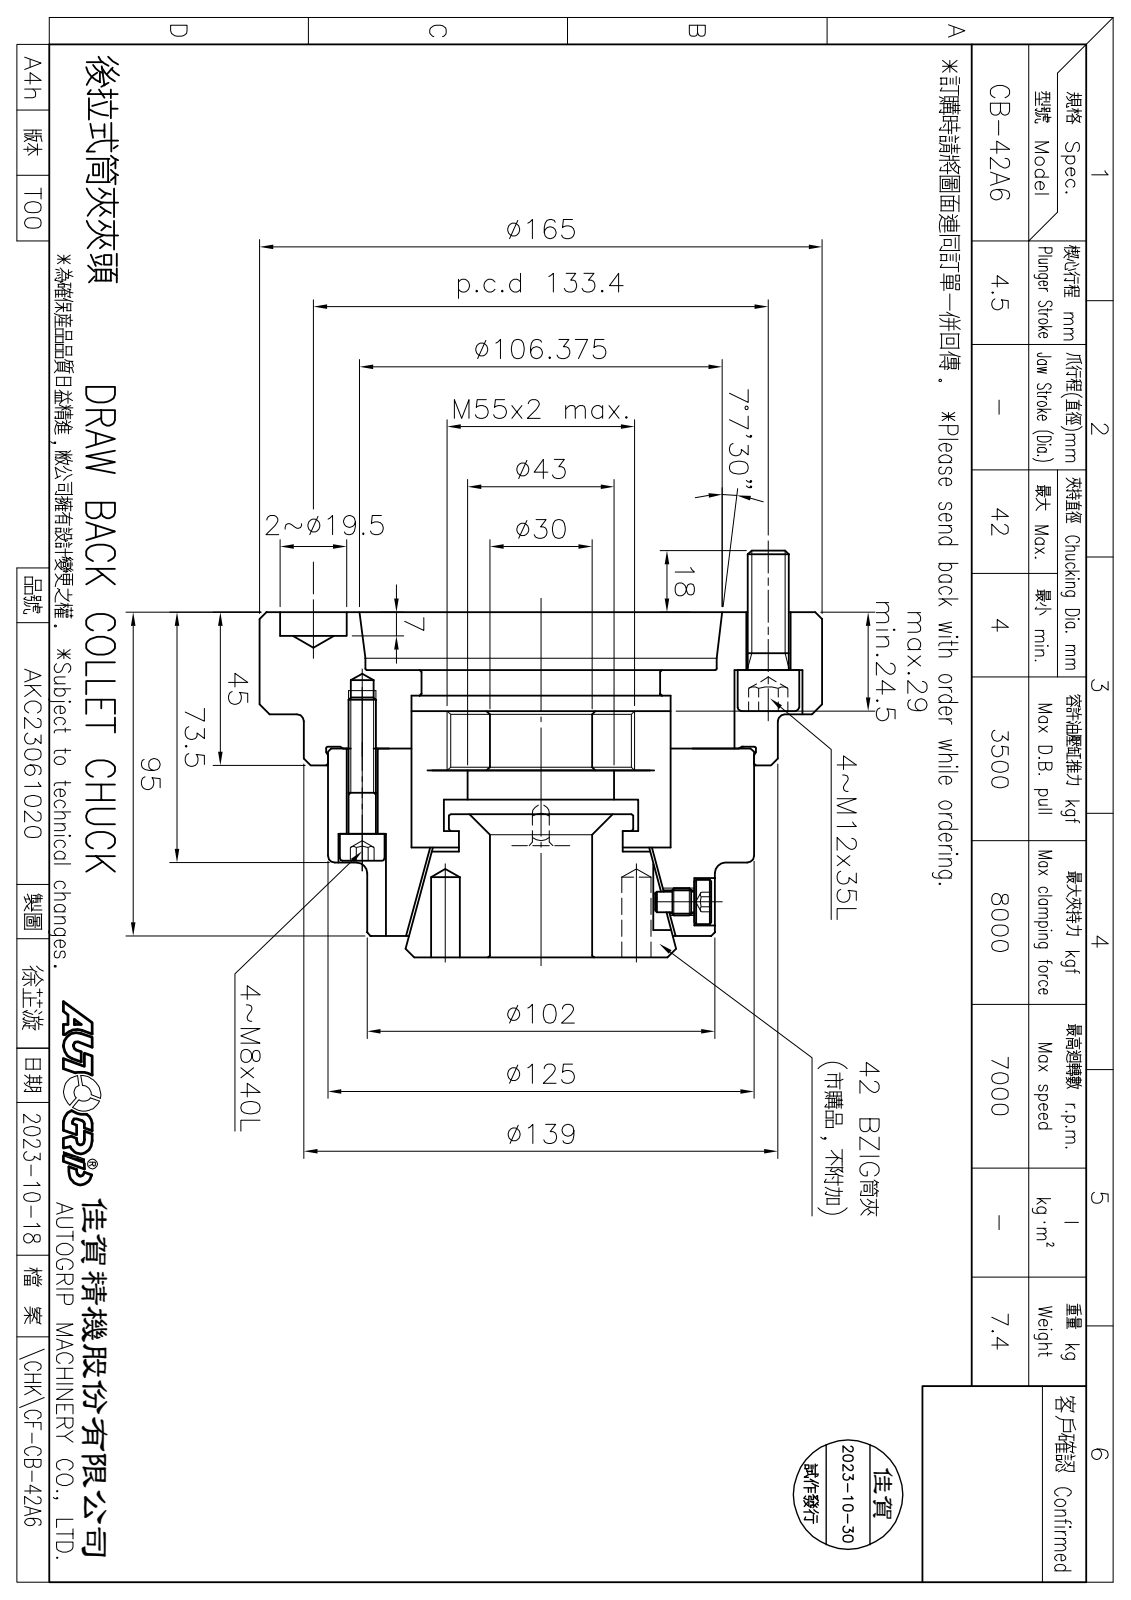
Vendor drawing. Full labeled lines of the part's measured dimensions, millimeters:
Part name (STEP PRODUCT): CF-RG-42R_RG42RM60; 圓頭內六角螺栓_M12x35; CF-CB-42A6-01020; CF-CB-42A6 (+3 more)
STEP written by: SolidWorks 2020 (CONFIG_CONTROL_DESIGN)
Units: millimetres
Bodies: 12 solids, 413 faces (152 planar, 133 cylindrical, 128 other)
Overall size (bounding box): 165 × 165 × 119.2
Volume: 1 097 000 mm³ · Surface area: 191 130 mm²
Round holes (diameter × count): ⌀5 ×4, ⌀6.8 ×4, ⌀9 ×4, ⌀13 ×4, ⌀14 ×4, ⌀20 ×4, ⌀8.5 ×3, ⌀19.5 ×2, ⌀29.7 ×1, ⌀43 ×1, ⌀50 ×1, ⌀53 ×1
Round bosses / shafts (diameter × count): ⌀18 ×4, ⌀13 ×4, ⌀12 ×4, ⌀8 ×4, ⌀165 ×1, ⌀139 ×1, ⌀102 ×1, ⌀54 ×1
Main face-to-face distances: 40, 23, 10, 29, 17, 30, 13, 69, 52, 39
Hole centre spacings: 37.89, 47.45, 66.7, 80.46, 90.03, 110.17, 21.7, 45
